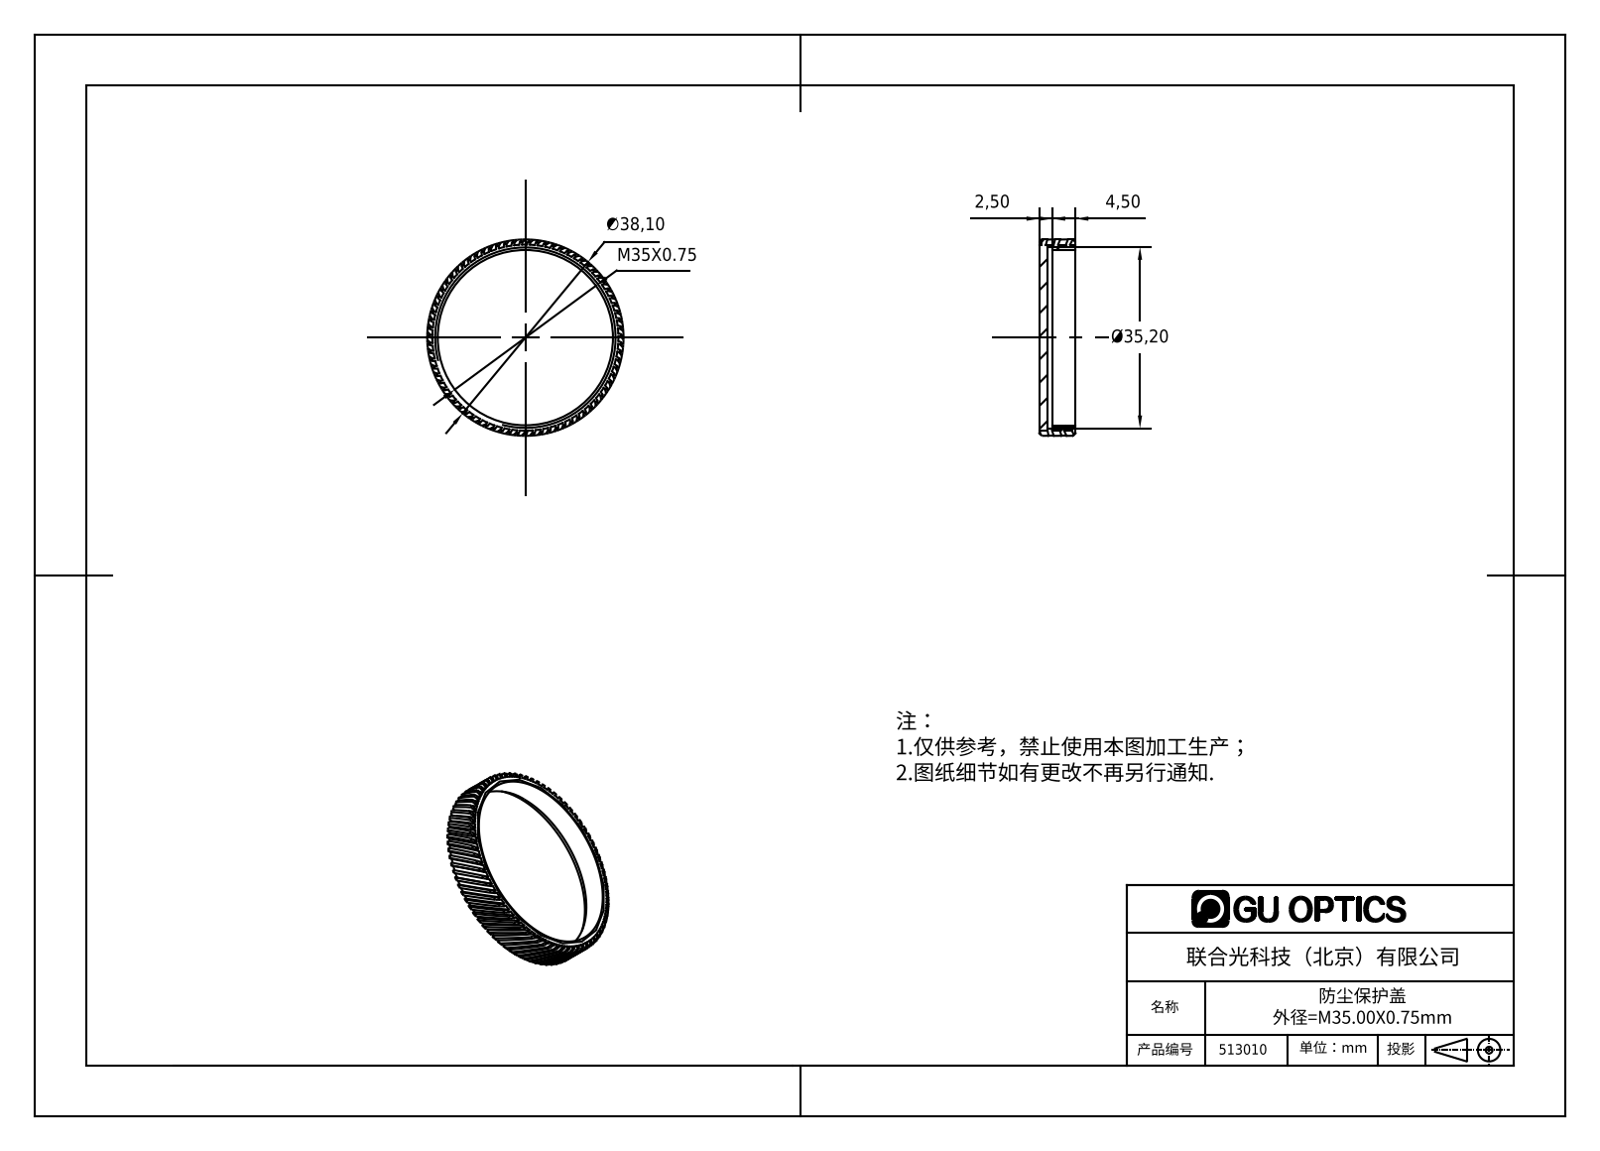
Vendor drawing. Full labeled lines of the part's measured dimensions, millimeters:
Part name (STEP PRODUCT): 513010
STEP written by: SolidWorks 2016 (AUTOMOTIVE_DESIGN)
Units: millimetres
Bodies: 1 solid, 462 faces (154 planar, 157 cylindrical, 151 other)
Overall size (bounding box): 38.1 × 38.1 × 7
Volume: 2 402 mm³ · Surface area: 4 892 mm²
Round holes (diameter × count): ⌀34 ×1, ⌀35.2 ×1
Round bosses / shafts (diameter × count): ⌀38.1 ×1, ⌀36.1 ×1
Main face-to-face distances: 1.5, 0.8, 5.5, 7, 4.5, 1, 2.5, 0.79
